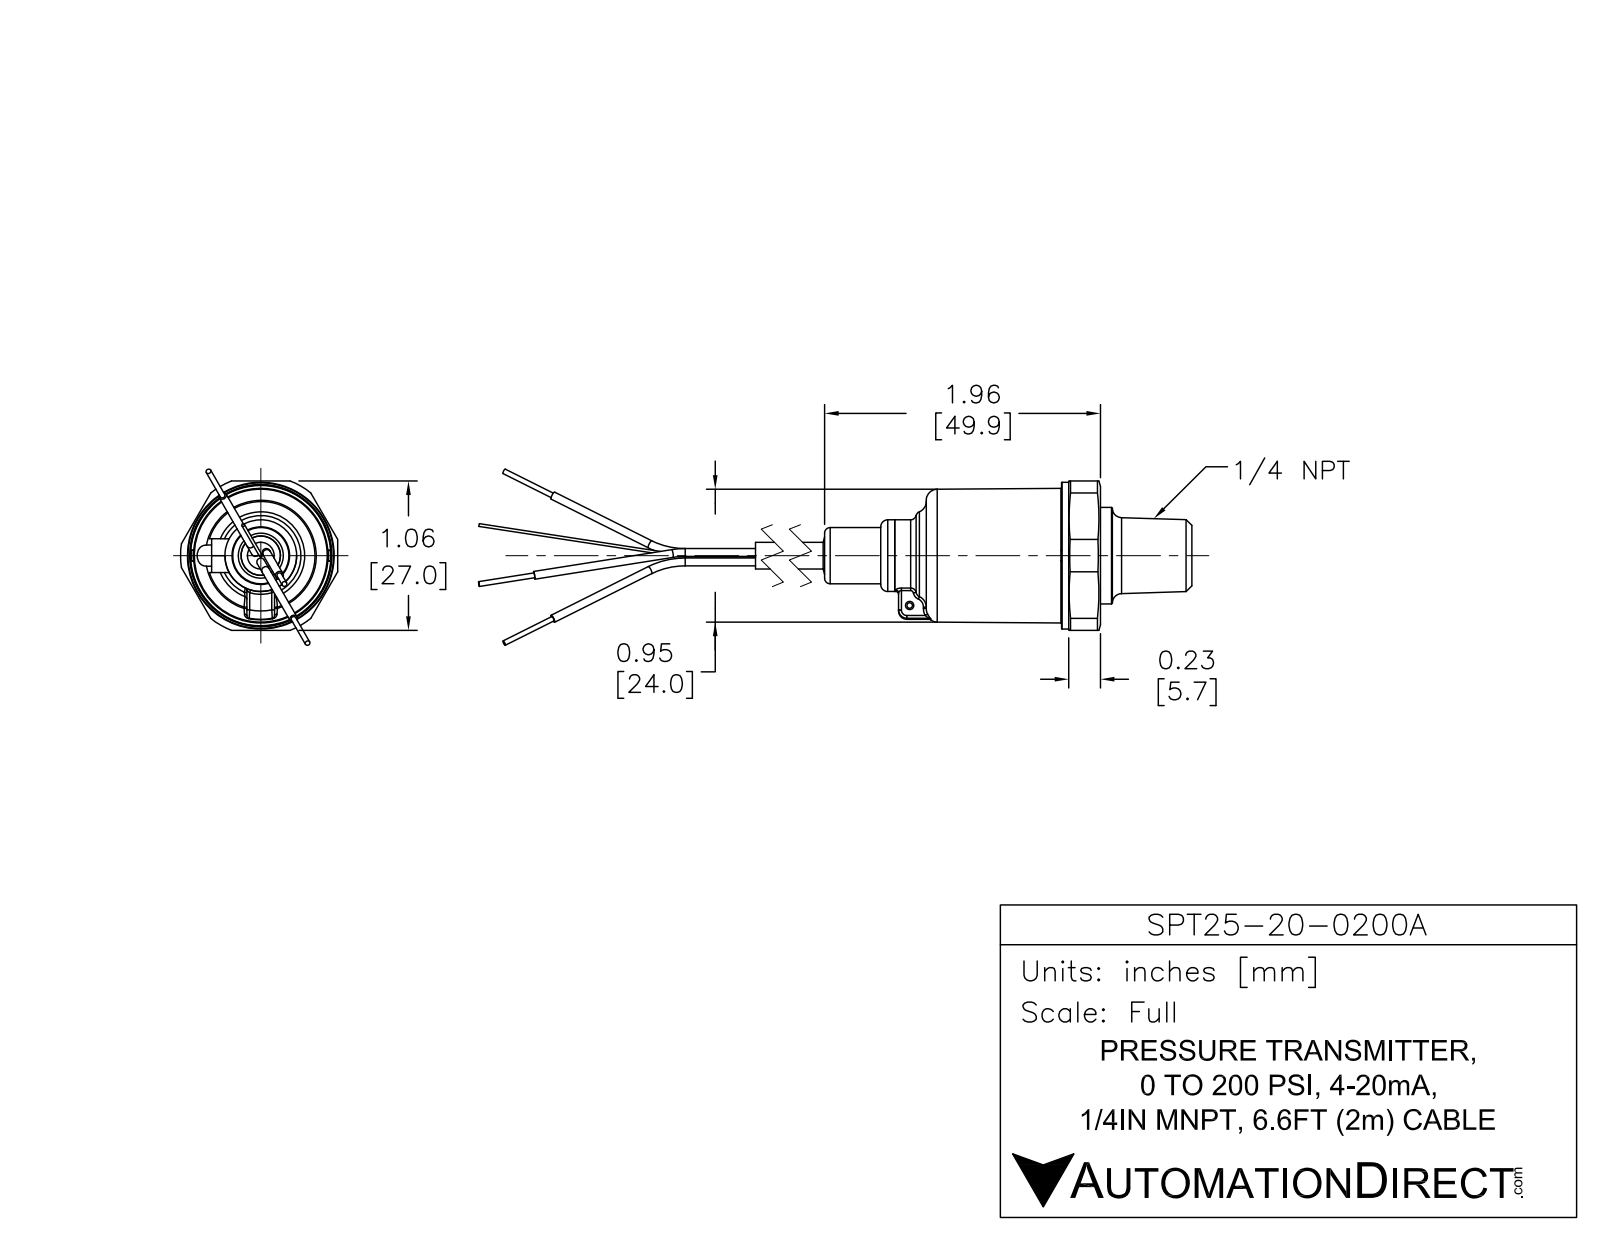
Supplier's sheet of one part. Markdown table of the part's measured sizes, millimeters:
| quantity | value |
| --- | --- |
| part name | SPT25-20-0200A |
| STEP written by | SolidWorks 2017 (AUTOMOTIVE_DESIGN) |
| units | millimeters |
| bodies | 7 solids, 116 faces (32 planar, 49 cylindrical, 35 other) |
| overall size | 153.3 × 29 × 27.09 |
| volume | 20 801 mm³ |
| surface area | 7 170 mm² |
| round holes (diameter × count) | 1 × 1, 3.3 × 1 |
| round bosses / shafts (diameter × count) | 1.4 × 6, 0.75 × 5, 26.75 × 1, 24 × 1, 17.5 × 1, 14 × 1, 13 × 1, 10 × 1 |
| partial cylindrical surfaces (radius × count) | 2 × 1, 14.5 × 1 |
| main face-to-face distances | 6.75, 24, 17.25, 42.75, 49.5, 66.75, 44, 1.25, 5.5, 22.75 |
